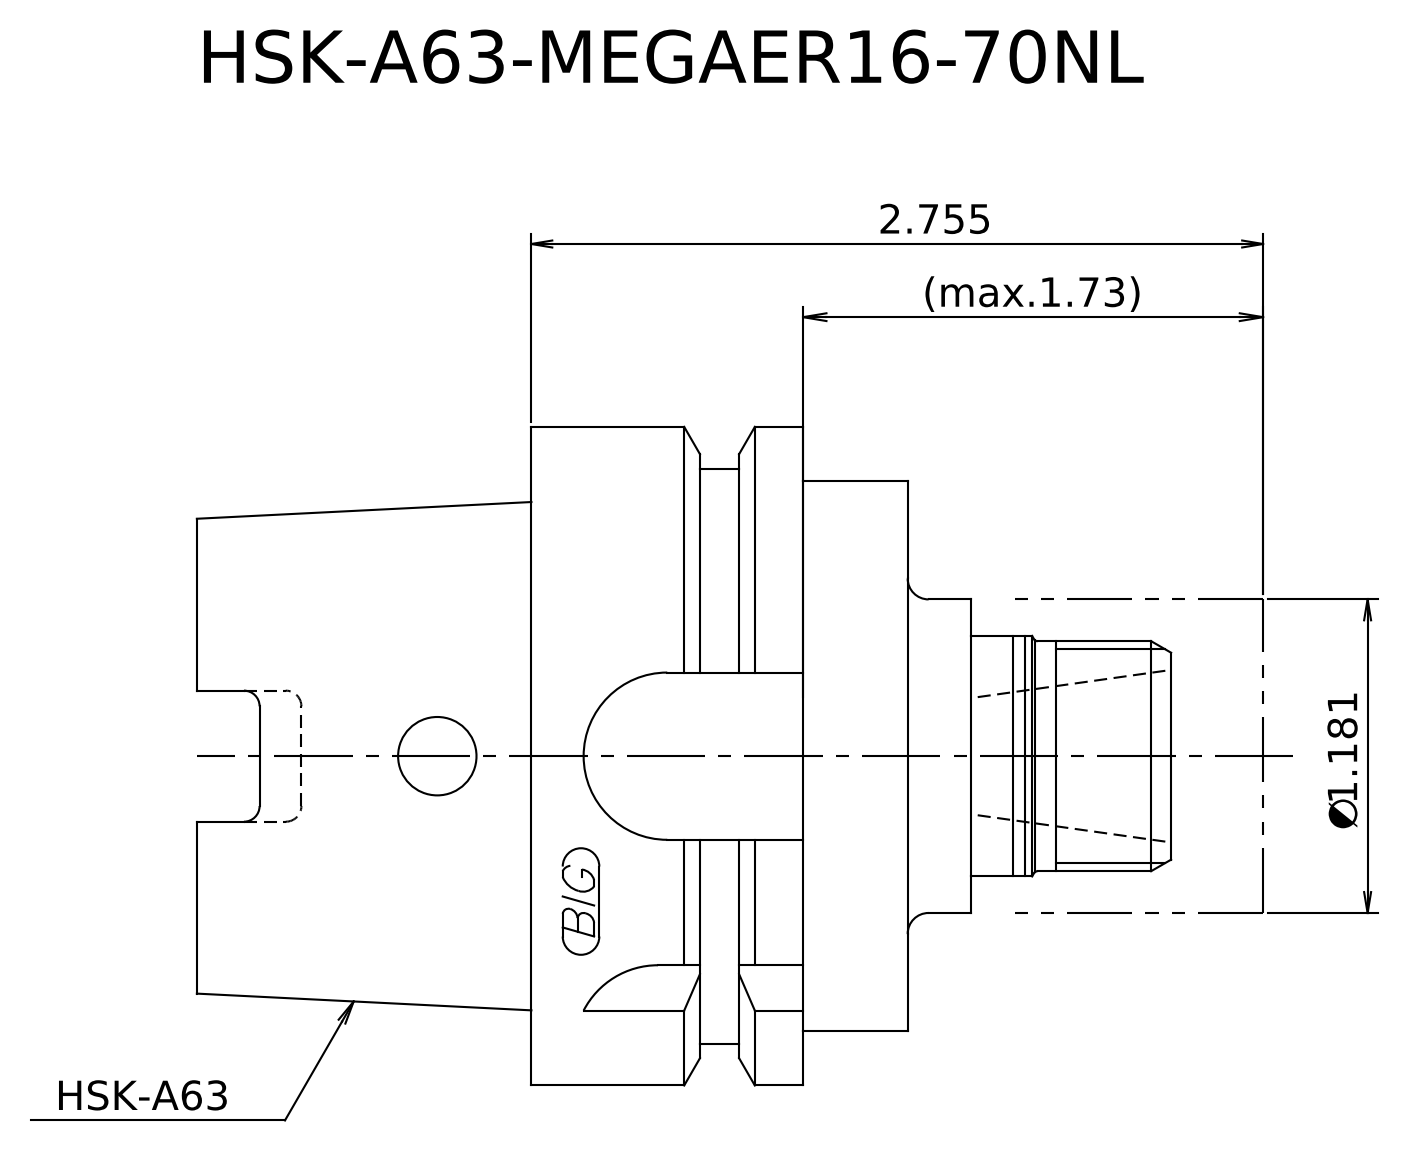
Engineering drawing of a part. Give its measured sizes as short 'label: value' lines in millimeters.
written by: Kubotek KeyCreator 2011 V10.0.2 (22737) (automotive_design)
unit: mm
bodies: 2 solids, 24 faces (10 planar, 8 cylindrical, 6 other)
size: 102 × 63 × 63
volume: 184 441 mm³; area: 23 975 mm²
bosses: 1× ⌀63, 1× ⌀55, 1× ⌀52.6, 1× ⌀30, 1× ⌀23, 1× ⌀22
face distances: 68, 36, 32, 10, 26, 58, 9, 19, 45, 77
